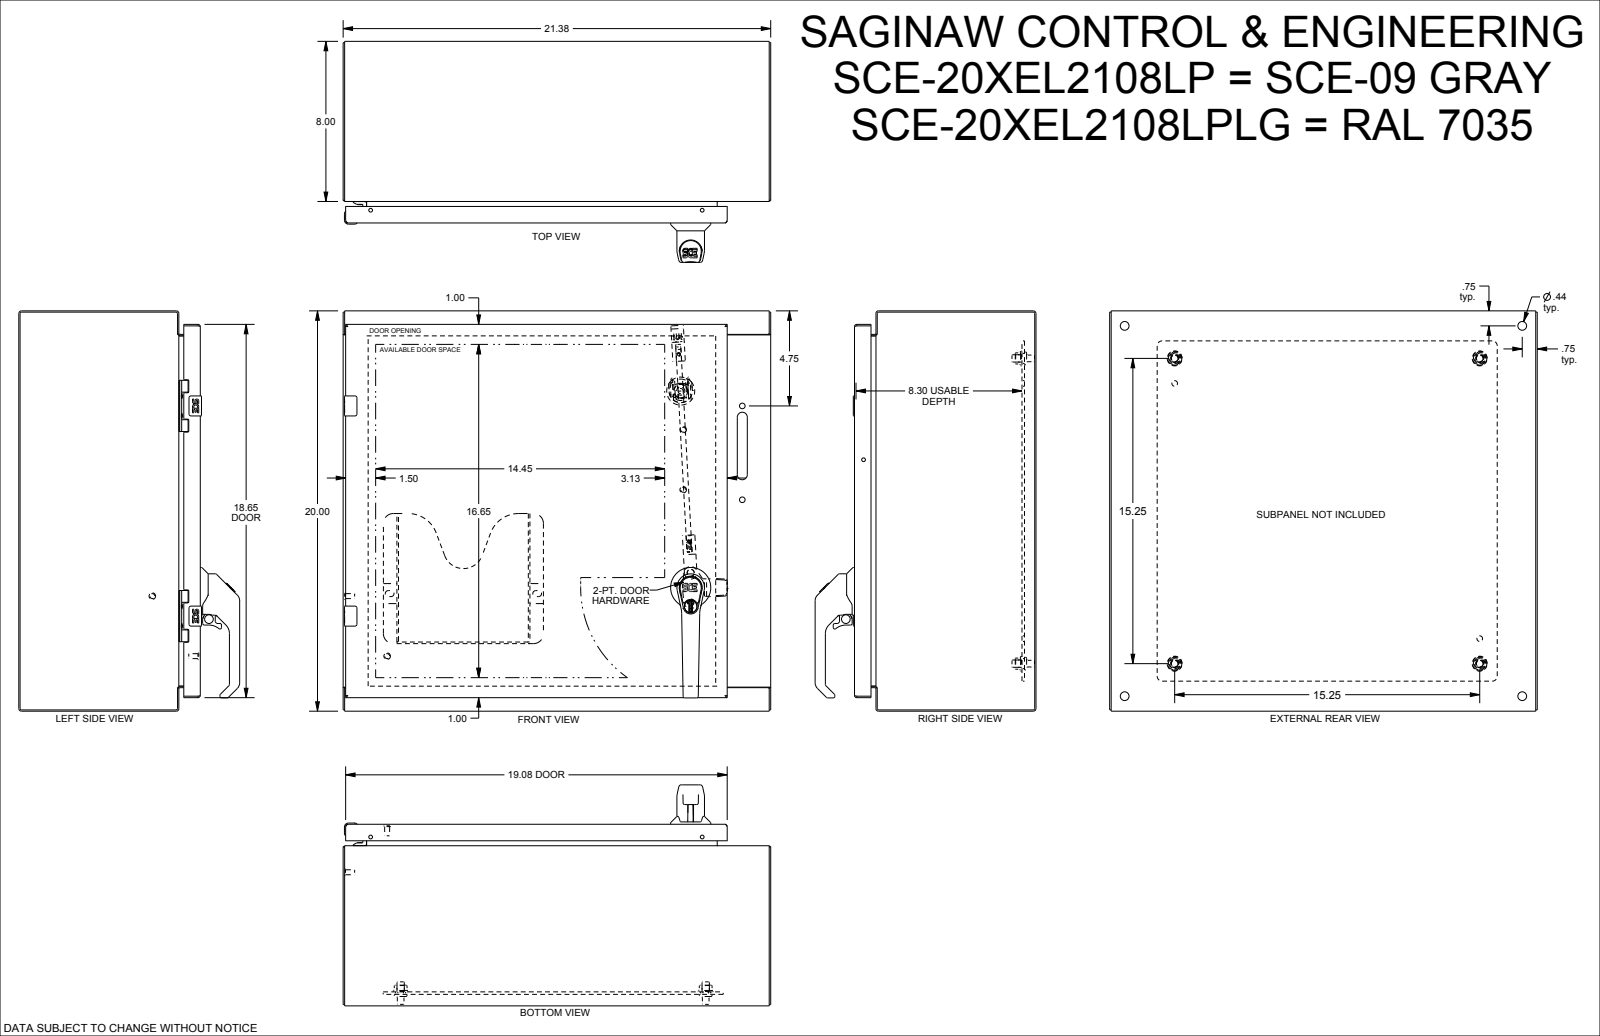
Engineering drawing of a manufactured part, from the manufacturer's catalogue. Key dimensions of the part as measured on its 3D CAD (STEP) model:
Part name (STEP PRODUCT): SCE-20XEL2108LPLG
STEP written by: SolidWorks 2021 (AUTOMOTIVE_DESIGN)
Units: inches
Bodies: 67 solids, 4458 faces (1625 planar, 1197 cylindrical, 1636 other)
Overall size (bounding box): 21.375 × 20 × 11.041
Volume: 182.1 in³ · Surface area: 4 352 in²
Round holes (diameter × count): ⌀0.266 ×5, ⌀0.172 ×4, ⌀0.205 ×4, ⌀0.244 ×4, ⌀0.281 ×4, ⌀0.367 ×4, ⌀0.375 ×4, ⌀0.437 ×4, ⌀0.5 ×4, ⌀0.25 ×3, ⌀0.04 ×2, ⌀0.138 ×2
Round bosses / shafts (diameter × count): ⌀0.248 ×7, ⌀0.17 ×6, ⌀0.366 ×4, ⌀0.332 ×4, ⌀0.25 ×4, ⌀0.24 ×4, ⌀0.563 ×3, ⌀0.196 ×3
Partial cylindrical surfaces — rounded edges, fillets, slot ends (radius × count): R0.03 ×67, R0.015 ×50, R0.02 ×43, R0.02 ×34, R0.01 ×32, R0.039 ×28, R0.005 ×26, R0.04 ×25
Main face-to-face distances: 0.075, 0.075, 8.998, 0.06, 9.073, 9.013, 8.938, 21.3, 0.125, 0.5
Hole centre spacings: 0.985, 15.25, 4.493, 10.5, 14.993, 0.02, 0.472, 0.493
